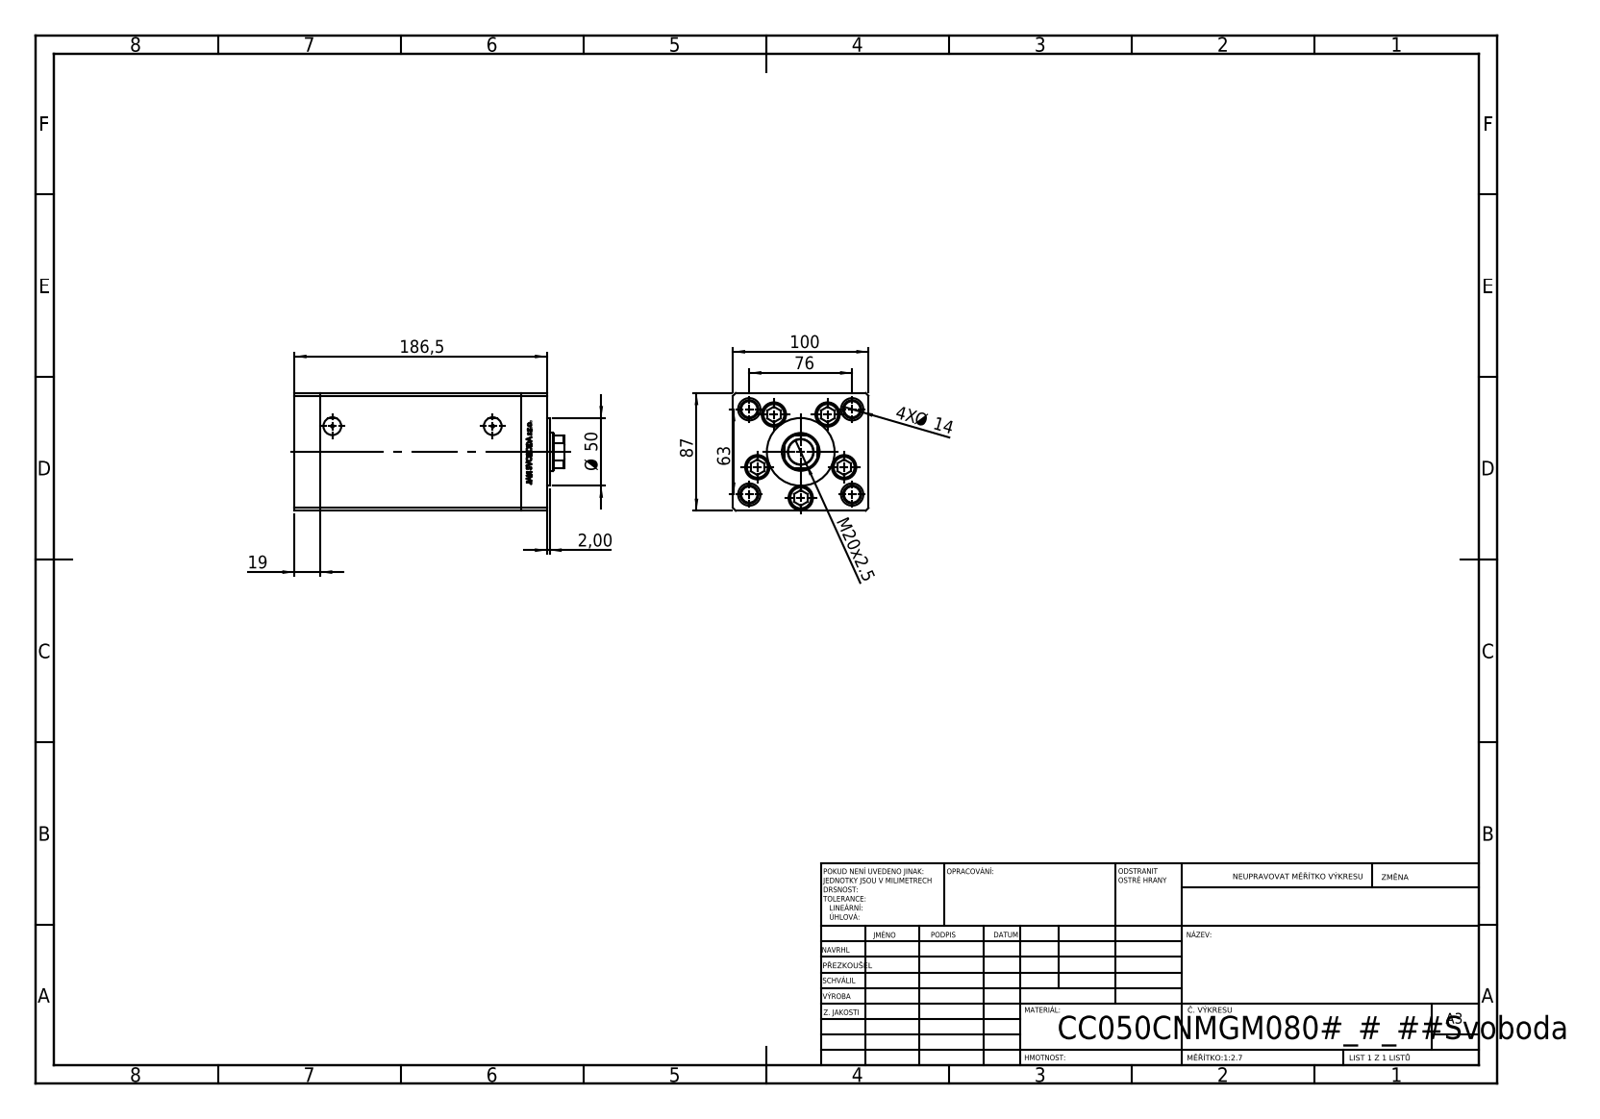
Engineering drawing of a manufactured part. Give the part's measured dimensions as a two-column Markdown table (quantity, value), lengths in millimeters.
| quantity | value |
| --- | --- |
| part name | V220C_C MIDDLE; V220C FRONT; ALLEN BOLT; V220C BACK_C (+1 more) |
| STEP written by | SolidWorks 2019 (CONFIG_CONTROL_DESIGN) |
| units | millimeters |
| bodies | 13 solids, 1172 faces (542 planar, 168 cylindrical, 462 other) |
| overall size | 199.5 × 100 × 87 |
| volume | 1 332 000 mm³ |
| surface area | 229 693 mm² |
| round holes (diameter × count) | 13.5 × 9, 18 × 5, 12 × 4, 16.5 × 4, 2 × 2, 13.16 × 2, 17 × 1, 18.5 × 1, 28 × 1 |
| round bosses / shafts (diameter × count) | 8 × 5, 17 × 4, 50 × 1 |
| partial cylindrical surfaces (radius × count) | 0.93 × 2, 13.5 × 1 |
| main face-to-face distances | 100, 87, 19, 148.5, 167.5, 34.25, 186.5, 152.25, 133.25, 15.25 |
| hole center spacings | 34, 49.36, 18.59, 21.03, 38.08, 39.27, 40.83, 43.24 |
